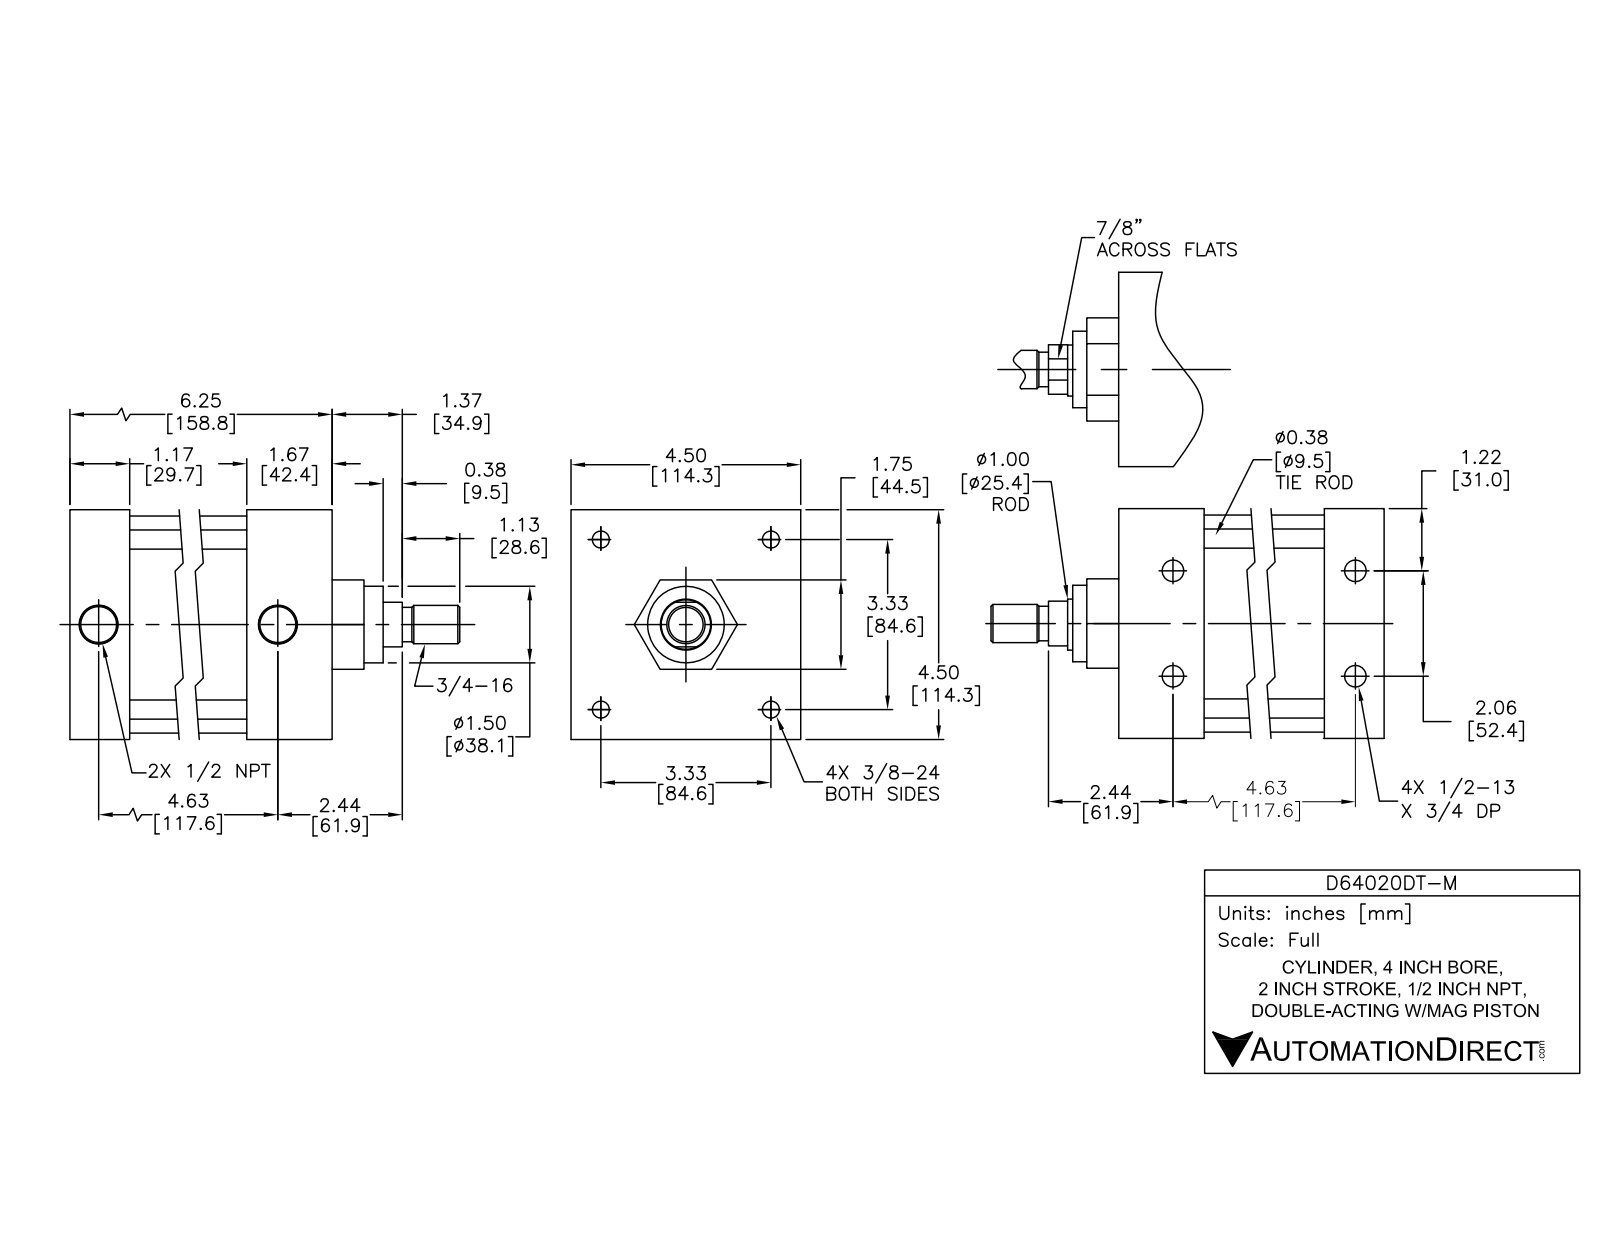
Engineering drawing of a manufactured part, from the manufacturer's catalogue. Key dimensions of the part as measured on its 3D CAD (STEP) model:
Part name (STEP PRODUCT): D64020DT-M PISTON; D64020DT-M; D64020DT-M BODY
STEP written by: SolidWorks 2015 (AUTOMOTIVE_DESIGN)
Units: inches
Bodies: 12 solids, 303 faces (99 planar, 114 cylindrical, 90 other)
Overall size (bounding box): 8.745 × 4.5 × 4.5
Volume: 82.87 in³ · Surface area: 357 in²
Round holes (diameter × count): ⌀0.33 ×4, ⌀0.406 ×4, ⌀0.417 ×4, ⌀0.625 ×4, ⌀0.5 ×2, ⌀0.766 ×2, ⌀1 ×1, ⌀1.003 ×1, ⌀4 ×1
Round bosses / shafts (diameter × count): ⌀0.609 ×4, ⌀0.375 ×4, ⌀0.34 ×4, ⌀4.25 ×1, ⌀3.997 ×1, ⌀1.75 ×1, ⌀0.997 ×1, ⌀0.97 ×1
Partial cylindrical surfaces — rounded edges, fillets, slot ends (radius × count): R0.45 ×4
Main face-to-face distances: 4.5, 0.08, 3.326, 6.246, 1.75, 4.997, 1.249, 3.751, 1.246, 2.495
Hole centre spacings: 1.031, 4.736, 4.622, 2.062, 2.349, 2.349, 3.322, 3.322
